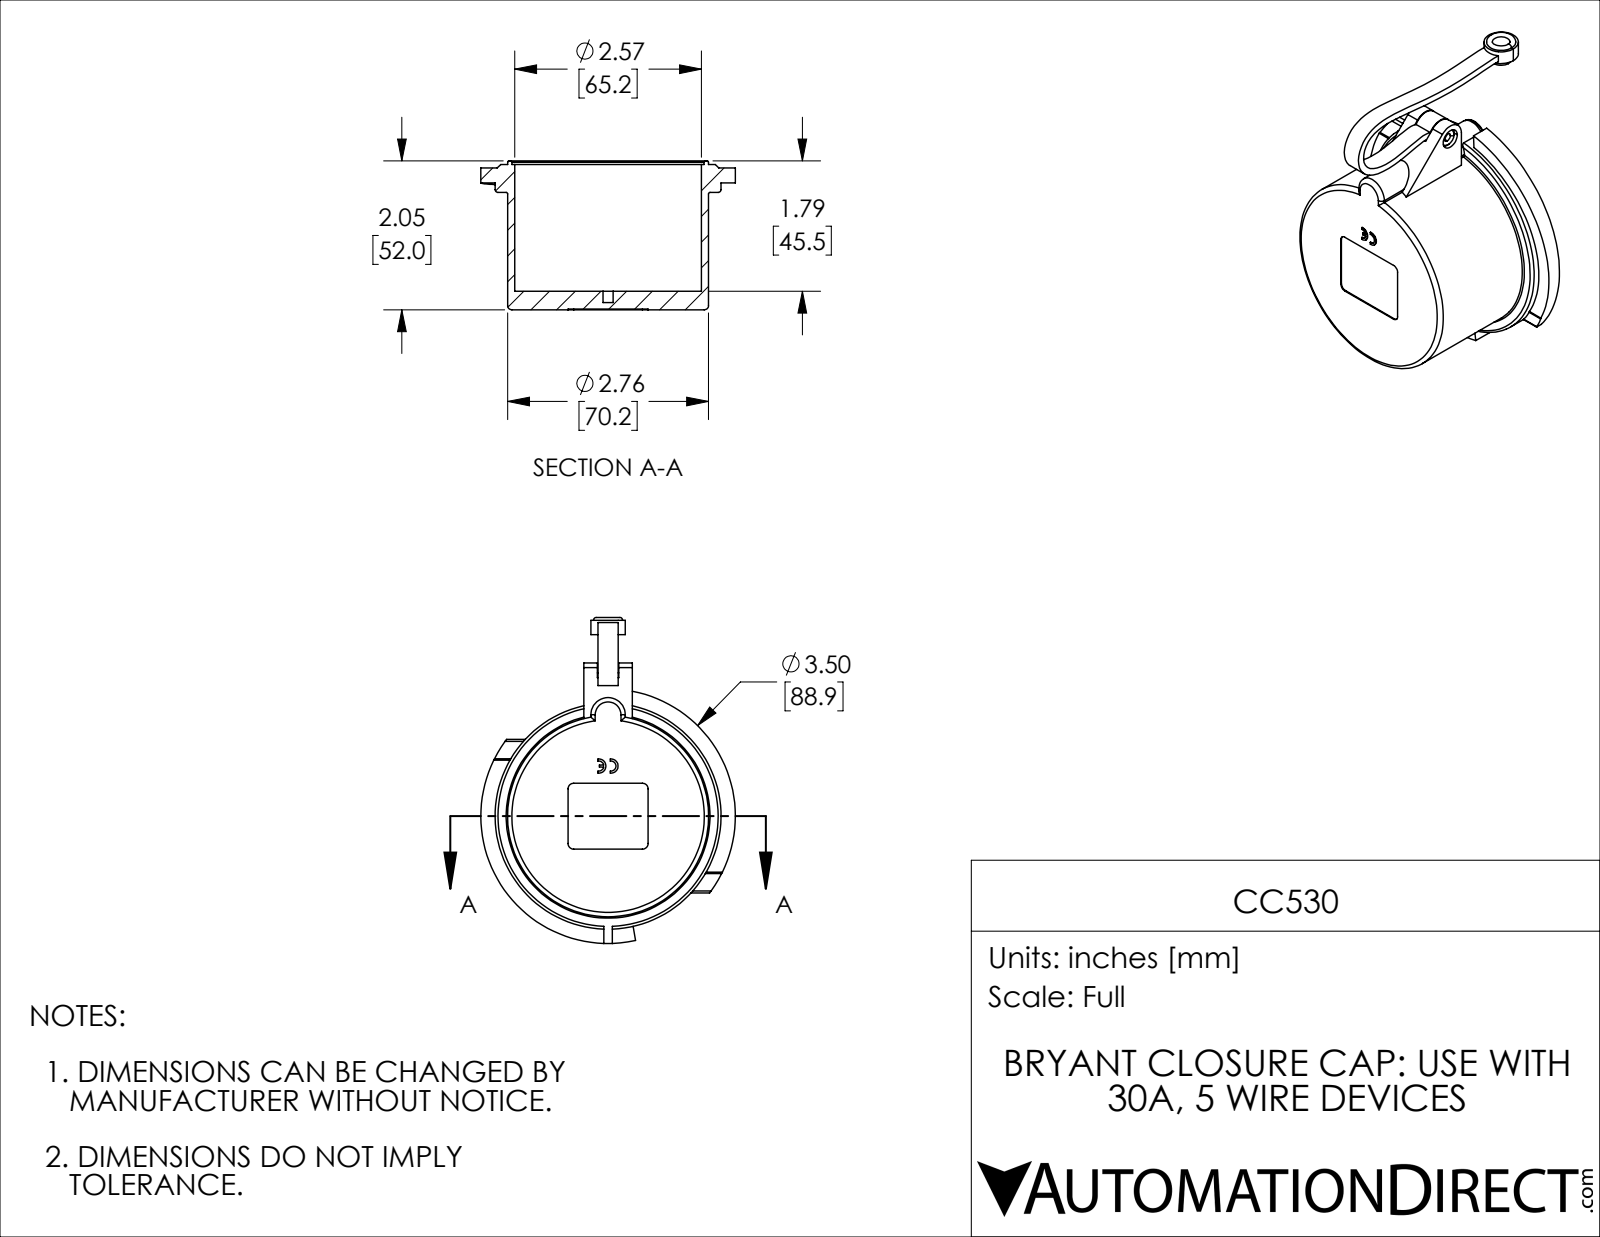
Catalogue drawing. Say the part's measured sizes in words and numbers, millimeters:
The part is named "CC530". Its 3-D file was written by "SolidWorks 2021 (CONFIG_CONTROL_DESIGN)". It is 2 solids with 182 faces: 59 planar, 82 cylindrical and 41 other. Overall it measures 113.8 by 88.9 by 80 millimeters. Its volume is 70 090 cubic millimeters and its surface area 38 190 square millimeters. Round holes: 1 of diameter 3, 1 of diameter 3.5, 1 of diameter 4.3, 1 of diameter 5, 1 of diameter 6.2, 1 of diameter 7, 1 of diameter 65.2, 1 of diameter 67.1. Round bosses or shafts: 1 of diameter 78.9, 1 of diameter 70.2, 1 of diameter 70.1, 1 of diameter 12, 1 of diameter 11, 1 of diameter 7, 1 of diameter 6, 1 of diameter 4. Partial cylindrical surfaces (rounded edges, fillets, slot ends): 8 of radius 2, 4 of radius 1, 2 of radius 1.5, 2 of radius 1.8, 2 of radius 2.5, 1 of radius 3.5, 1 of radius 4.4, 1 of radius 5.9. The main face-to-face distances are 6.5, 49.5, 43, 1.2, 50.7, 44.2, 5, 9.8, 8.5, 34.5.
